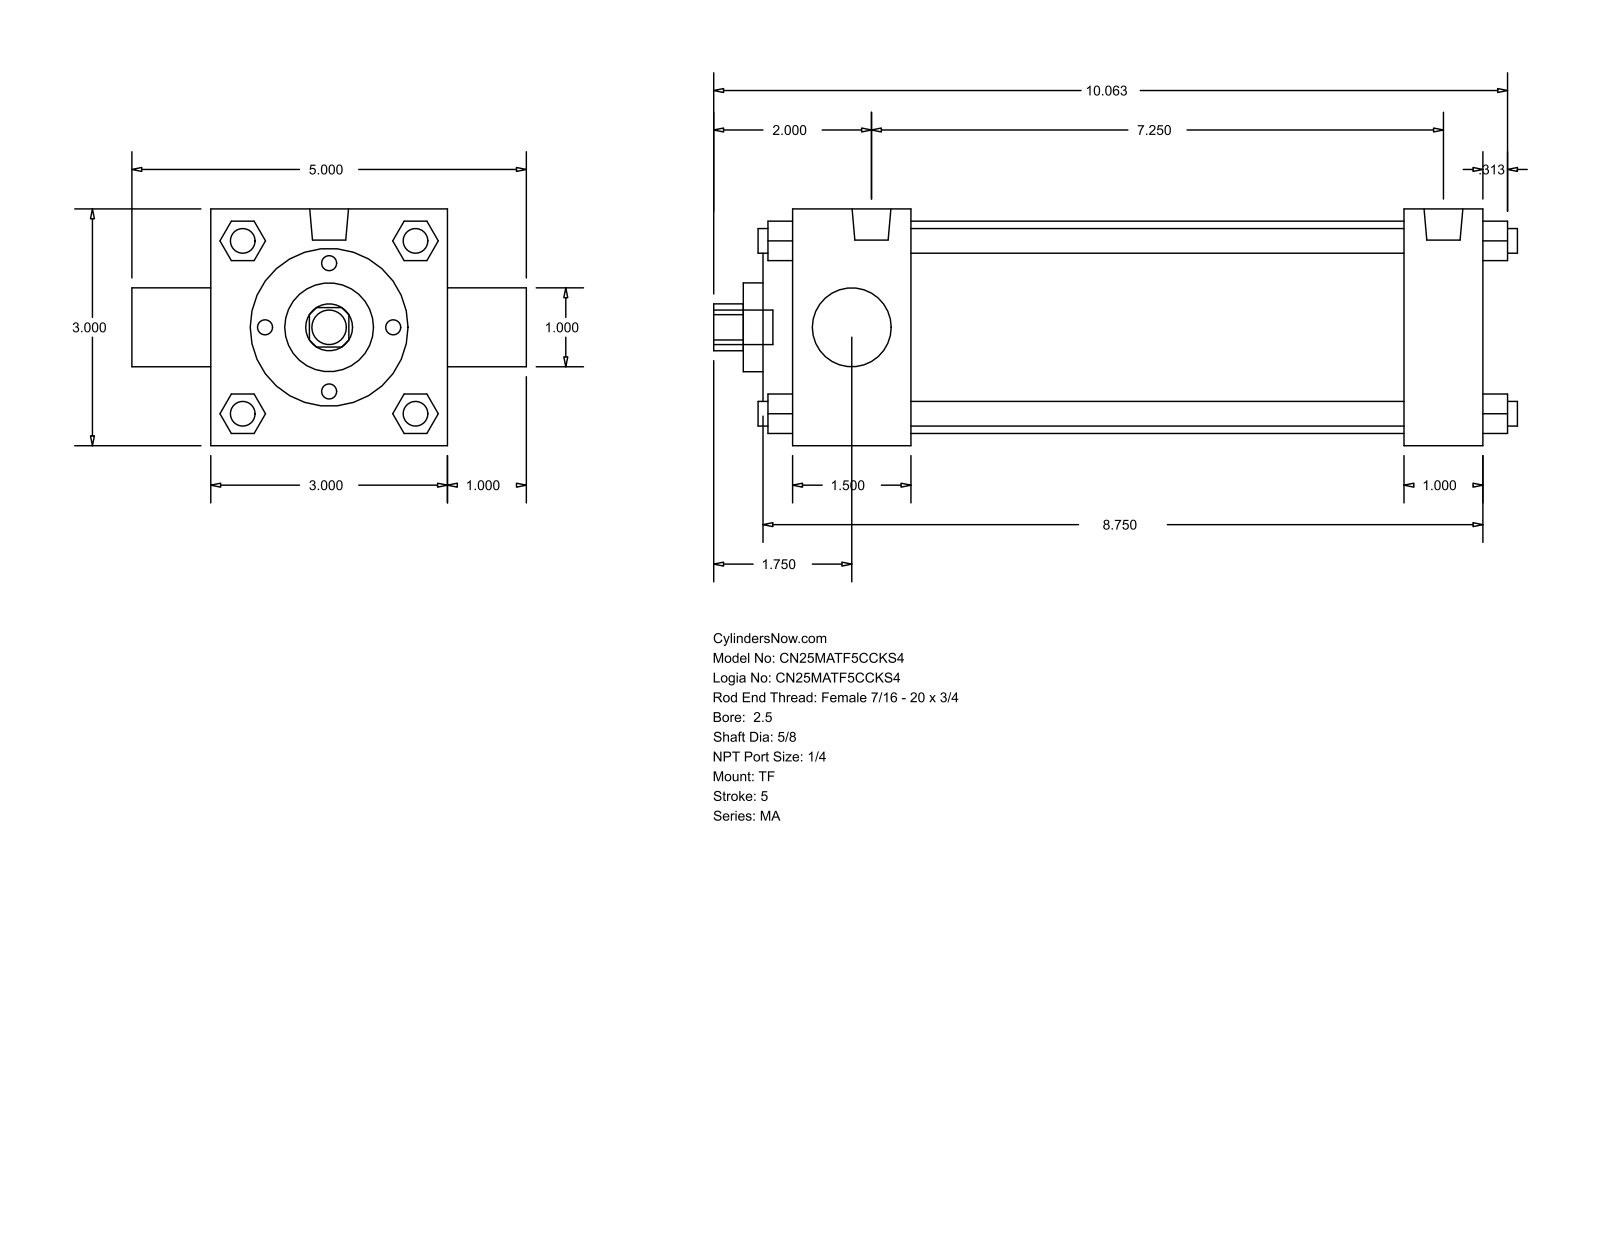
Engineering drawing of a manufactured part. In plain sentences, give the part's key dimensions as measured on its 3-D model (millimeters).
The part is named "MA_TF__0250_0.625". Its 3-D file was written by "GSSL Pune (CONFIG_CONTROL_DESIGN)". It is 0 solids with 122 faces: 93 planar, 29 cylindrical and 0 other. Overall it measures 258.76 by 127 by 76.2 millimeters. Round holes: 1 of diameter 15.88, 1 of diameter 25.4, 1 of diameter 28.57, 1 of diameter 50.8, 1 of diameter 68.33. Round bosses or shafts: 7 of diameter 7.94, 2 of diameter 12.49, 1 of diameter 11.11. Partial cylindrical surfaces (rounded edges, fillets, slot ends): 1 of radius 7.54. The main face-to-face distances are 76.2, 222.25, 25.4, 38.1, 196.85, 158.75, 184.15, 12.7, 9.52, 47.62.
